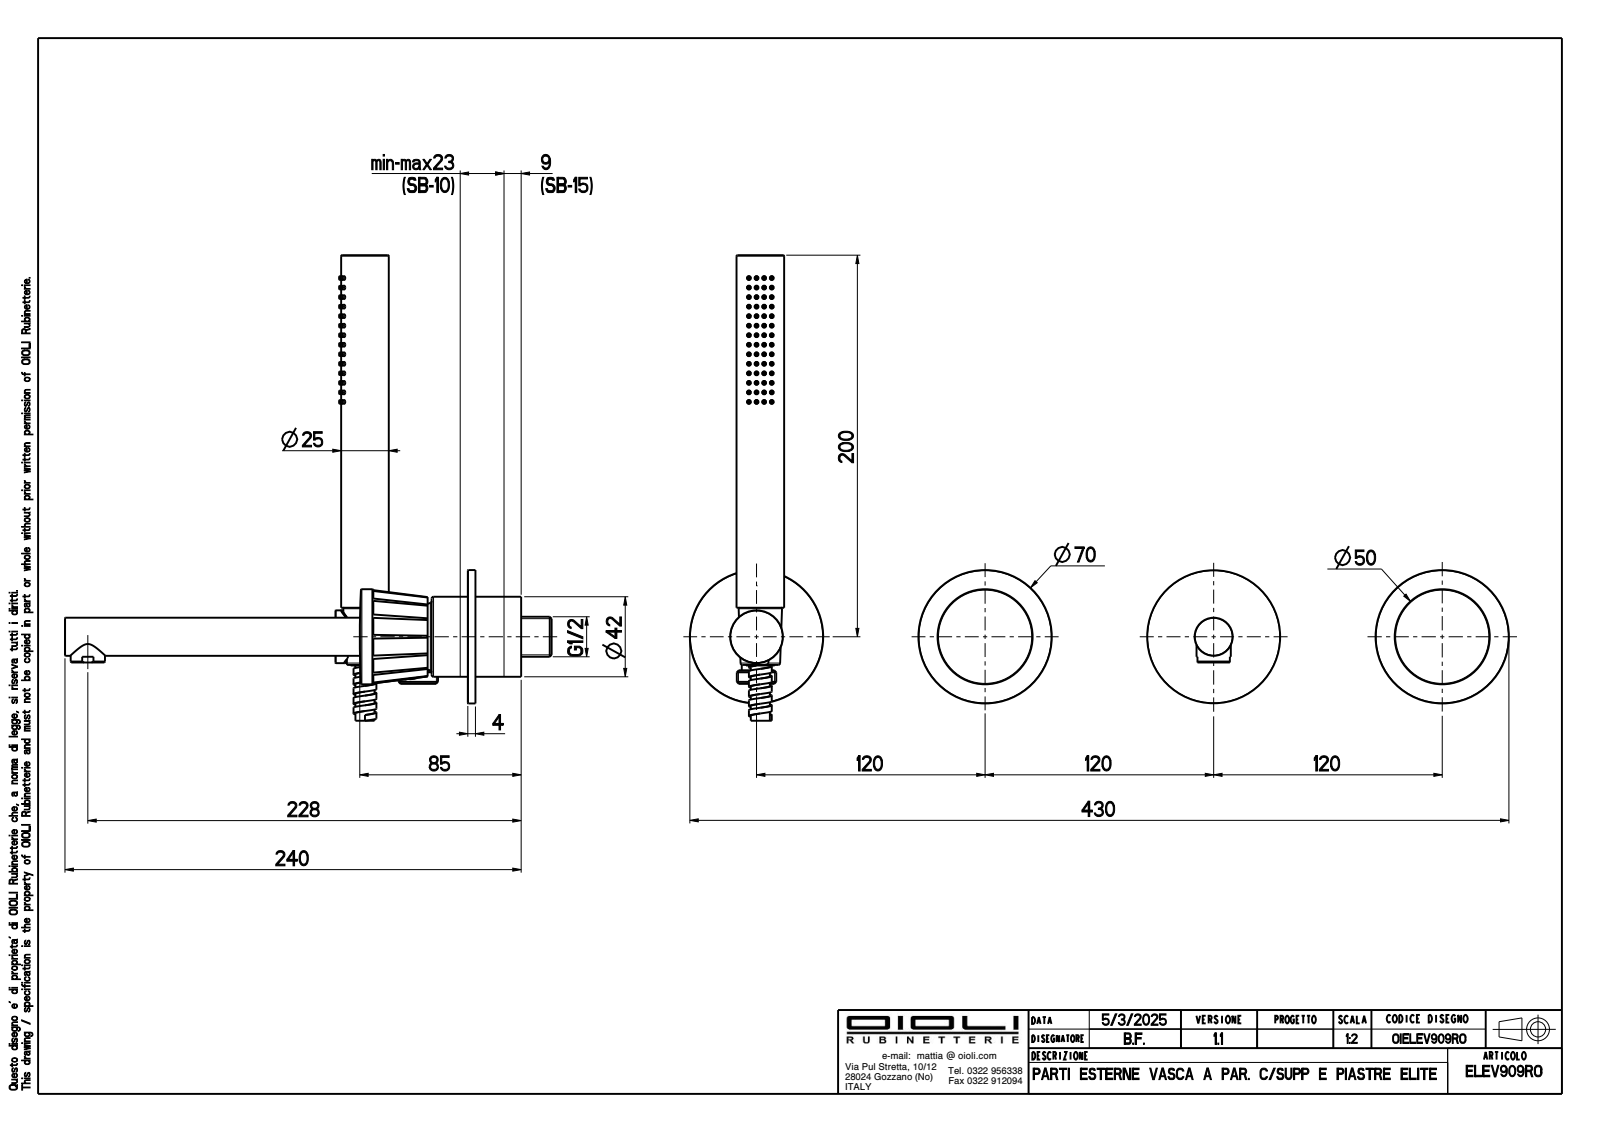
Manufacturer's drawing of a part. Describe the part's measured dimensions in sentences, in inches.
The part is named "OIBR00949; OIBR00242; OIBR00948; OIAQ00013 (+8 more)". Its 3-D file was written by "CREO PARAMETRIC BY PTC INC, 2024493 (CONFIG_CONTROL_DESIGN)". It is 21 solids with 1054 faces: 246 planar, 375 cylindrical and 433 other. Overall it measures 20.83 by 18.339 by 12.148 inches. Its volume is 16.54 cubic inches and its surface area 246.8 square inches. Round holes: 4 of diameter 0.165, 3 of diameter 0.61, 3 of diameter 0.669, 2 of diameter 0.157, 2 of diameter 0.209, 2 of diameter 0.256, 2 of diameter 0.374, 2 of diameter 0.433, 2 of diameter 0.571, 2 of diameter 0.591, 2 of diameter 1.181, 2 of diameter 1.555. Round bosses or shafts: 5 of diameter 0.197, 3 of diameter 2.756, 3 of diameter 0.709, 3 of diameter 0.65, 2 of diameter 1.965, 2 of diameter 1.654, 1 of diameter 2.748, 1 of diameter 1.24. Partial cylindrical surfaces (rounded edges, fillets, slot ends): 20 of radius 0.004, 4 of radius 0.197, 4 of radius 0.268, 2 of radius 0.394, 1 of radius 0.151, 1 of radius 0.157, 1 of radius 0.429, 1 of radius 0.531. The main face-to-face distances are 0.301, 0.157, 1.581, 0.079, 0.138, 1.443, 1.659, 1.522, 1.299, 1.6. The hole center spacings are 0.185, 0.514, 0.701, 1.105, 1.805, 5.237, 5.24, 5.309.
